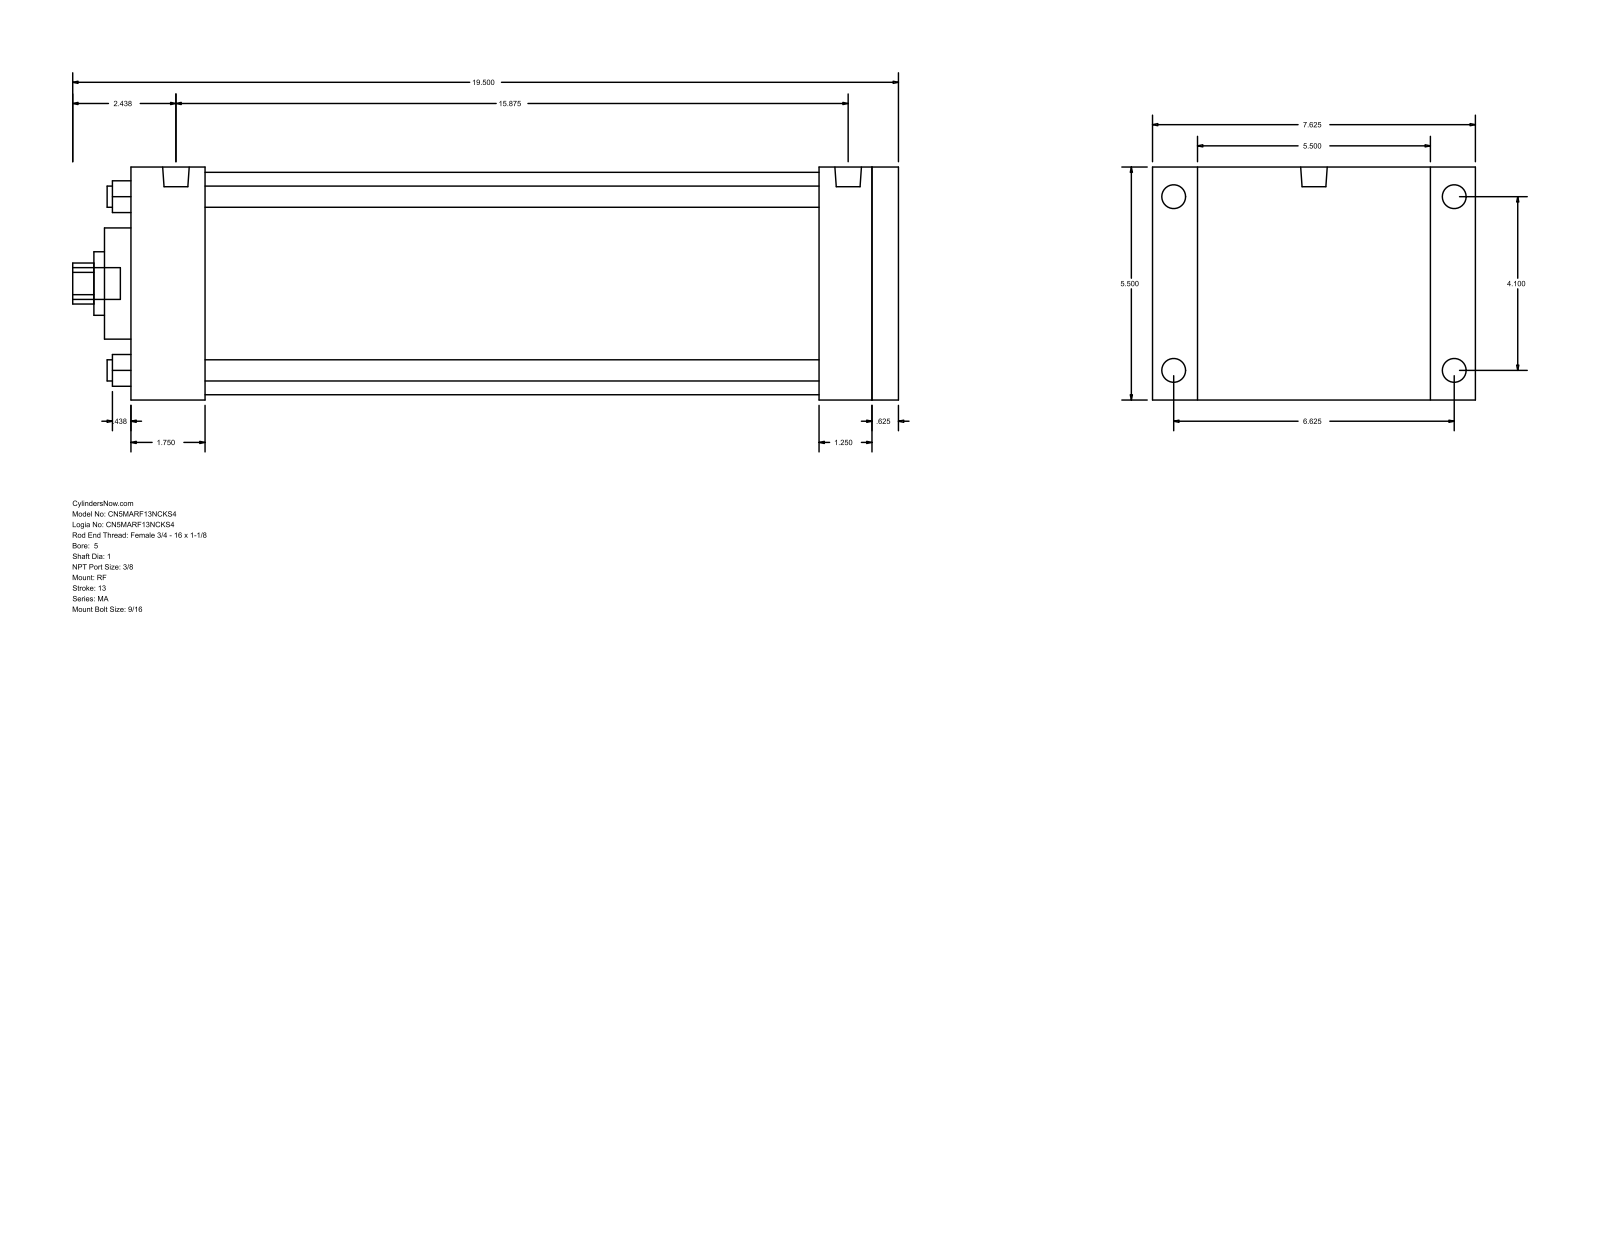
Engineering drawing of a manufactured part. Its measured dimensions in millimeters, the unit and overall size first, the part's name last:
Units: millimetres
Overall size (bounding box): 495.3 × 193.68 × 139.7
Round holes (diameter × count): ⌀12.7 ×4, ⌀25.4 ×1, ⌀38.1 ×1, ⌀66.67 ×1, ⌀133.35 ×1
Round bosses / shafts (diameter × count): ⌀14.29 ×4, ⌀11.11 ×4, ⌀15.93 ×2, ⌀19.05 ×1
Partial cylindrical surfaces — rounded edges, fillets, slot ends (radius × count): R12.29 ×1
Main face-to-face distances: 139.7, 460.38, 15.87, 444.51, 44.46, 400.05, 415.92, 412.76, 368.3, 31.75
Hole centre spacings: 73.64, 104.14, 147.28
Bodies: 0 solids, 94 faces (65 planar, 29 cylindrical, 0 other)
Part name (STEP PRODUCT): MA_RF__0500_1
STEP written by: GSSL Pune (CONFIG_CONTROL_DESIGN)
